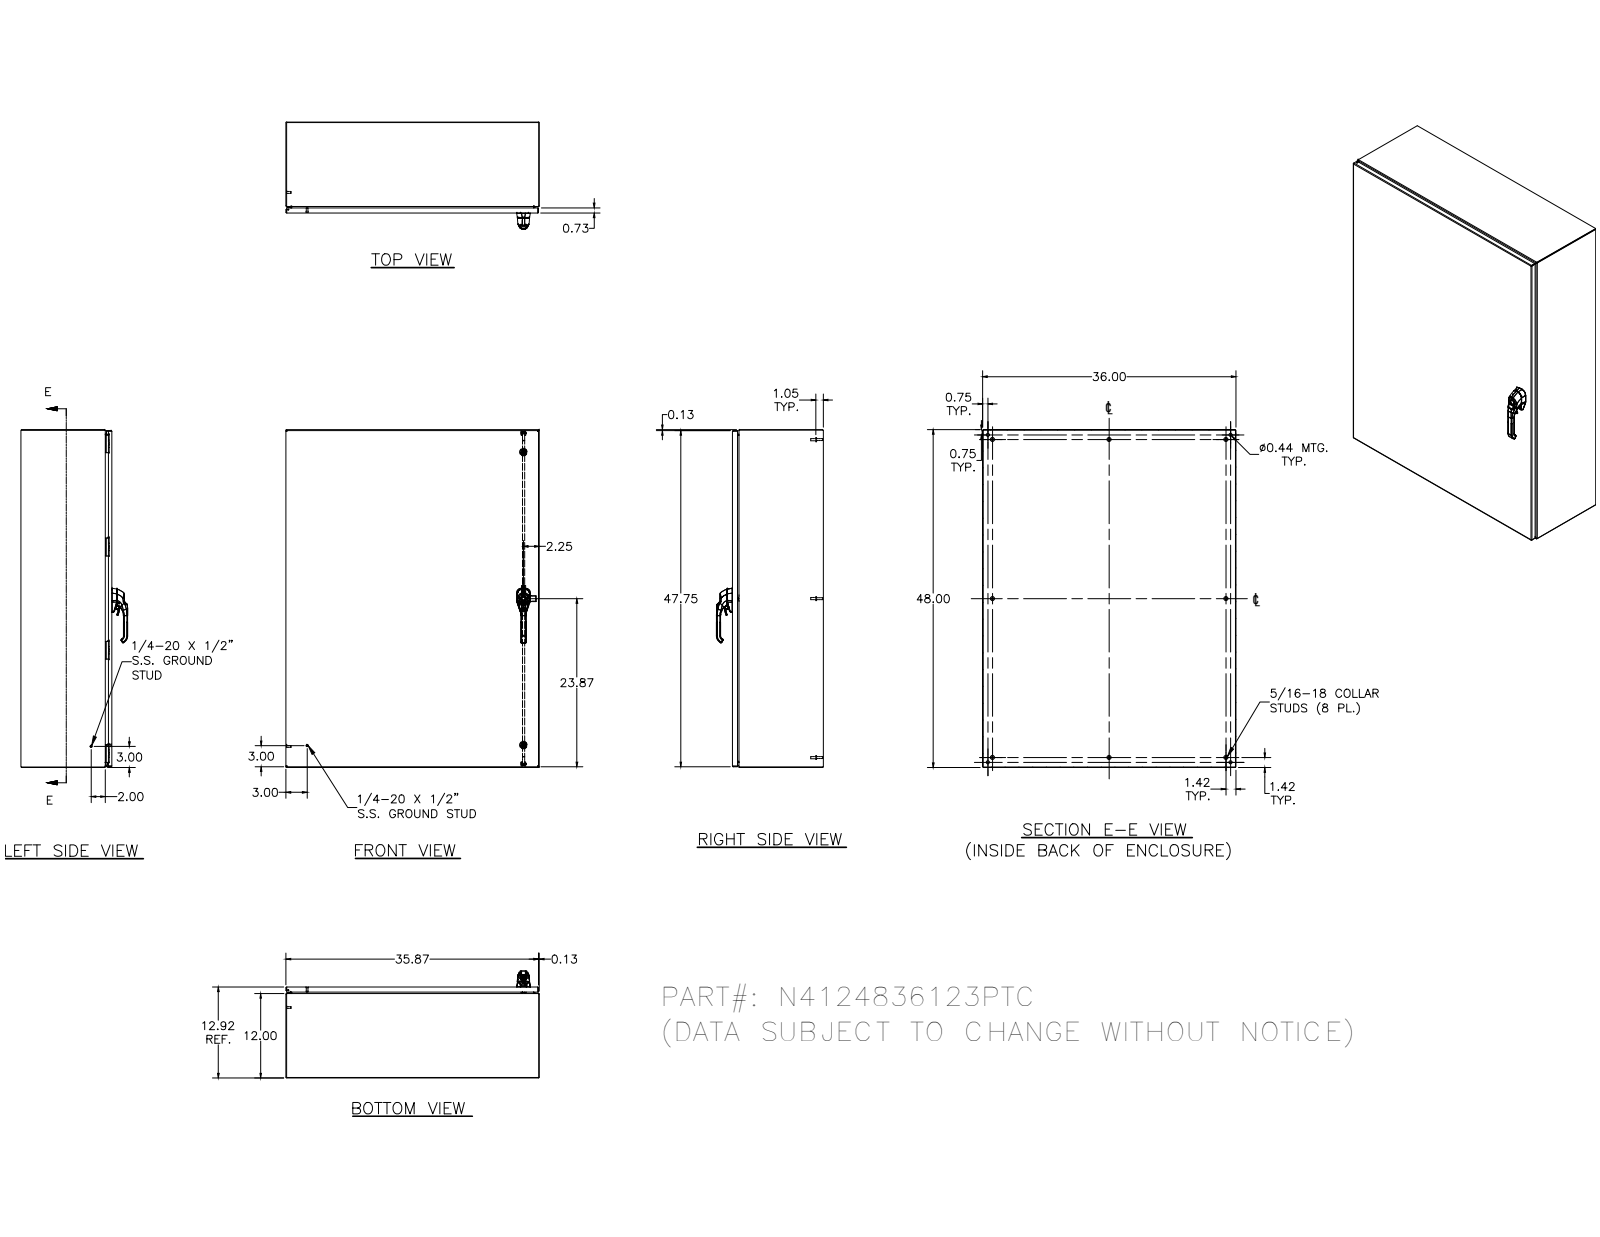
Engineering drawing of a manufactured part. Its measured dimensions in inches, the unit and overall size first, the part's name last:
Units: inches
Overall size (bounding box): 48 × 36 × 15.095
Round holes (diameter × count): ⌀0.188 ×9, ⌀0.093 ×8, ⌀0.152 ×8, ⌀0.167 ×8, ⌀0.172 ×8, ⌀0.156 ×4, ⌀0.165 ×4, ⌀0.197 ×4, ⌀0.438 ×4, ⌀0.106 ×2, ⌀0.16 ×2, ⌀0.169 ×2
Round bosses / shafts (diameter × count): ⌀0.25 ×18, ⌀0.563 ×8, ⌀0.36 ×8, ⌀0.32 ×8, ⌀0.3 ×8, ⌀0.256 ×8, ⌀0.164 ×8, ⌀0.131 ×8
Partial cylindrical surfaces — rounded edges, fillets, slot ends (radius × count): R0.05 ×50, R0.031 ×36, R0.016 ×34, R0.125 ×28, R0.02 ×18, R0.105 ×18, R0.032 ×16, R0.118 ×16
Main face-to-face distances: 0.074, 12.843, 12.917, 12.769, 35.926, 47.926, 35.852, 36, 47.852, 48
Hole centre spacings: 14.667, 29.333, 44, 0.66, 0.017, 14.667, 0.5, 0.656
Volume: 444.7 in³ · Surface area: 11 777 in²
Bodies: 75 solids, 2490 faces (837 planar, 932 cylindrical, 721 other)
Part name (STEP PRODUCT): N4124836123PTC
STEP written by: SolidWorks 2019 (AUTOMOTIVE_DESIGN)
